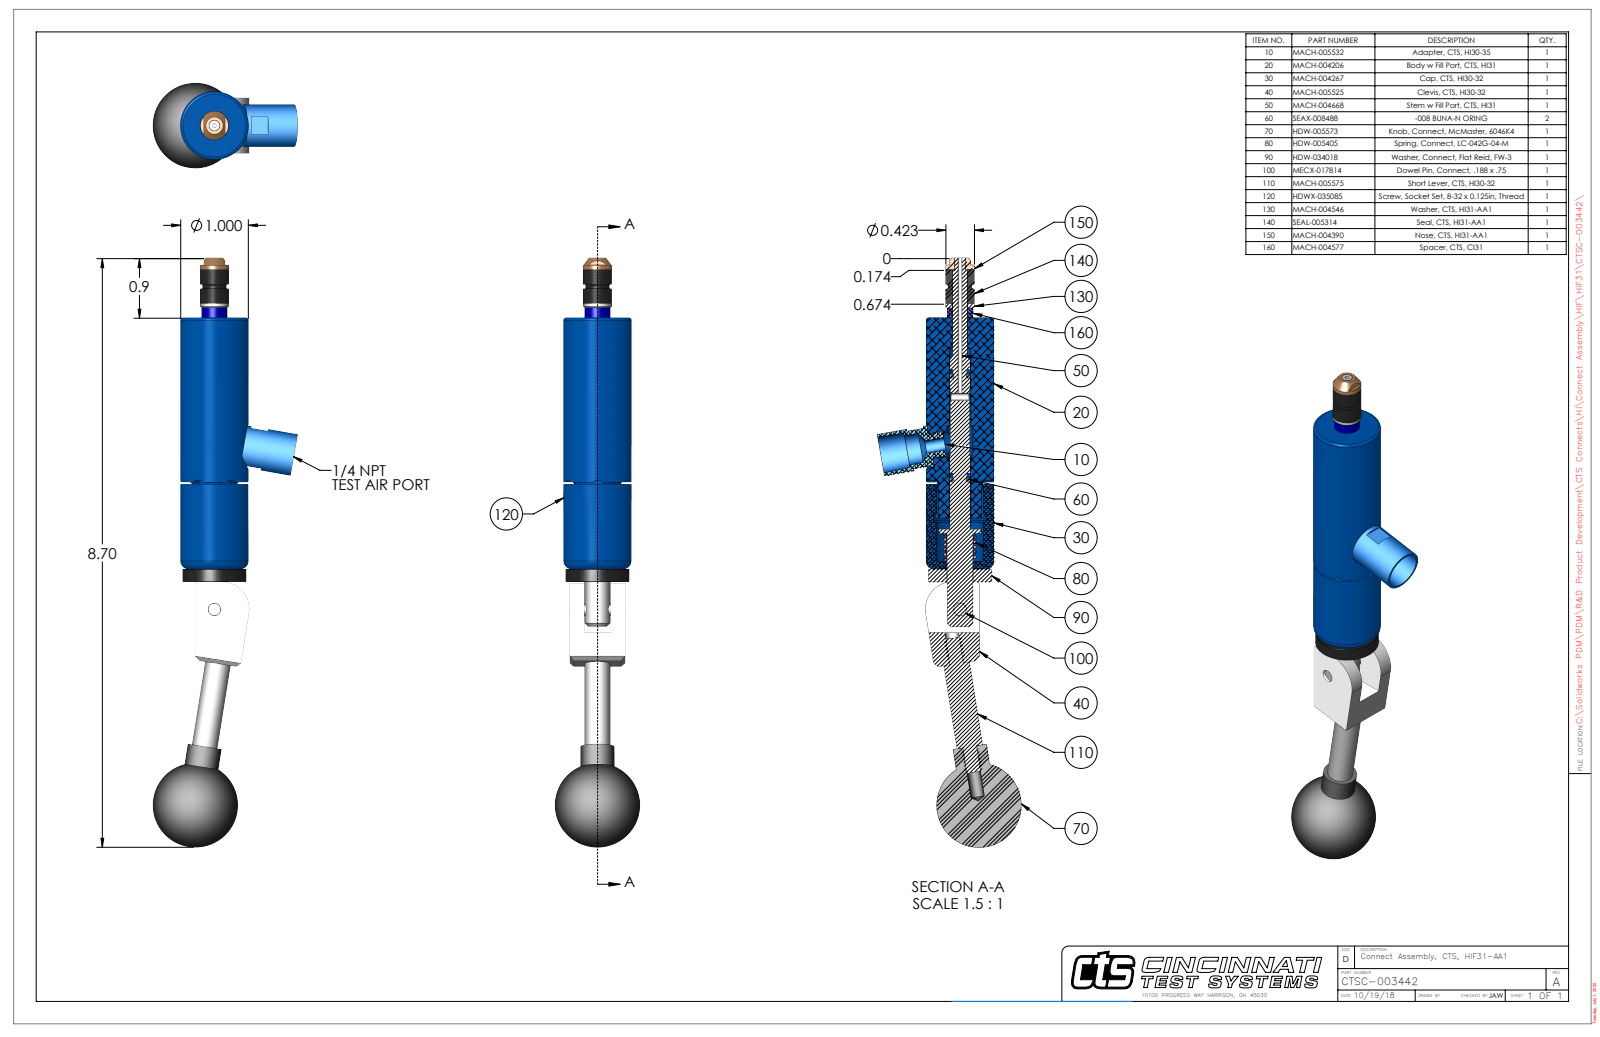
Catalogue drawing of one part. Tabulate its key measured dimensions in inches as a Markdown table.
| quantity | value |
| --- | --- |
| part name | CTSC-003442 |
| STEP written by | SolidWorks 2023 (AUTOMOTIVE_DESIGN) |
| units | inches |
| bodies | 10 solids, 281 faces (98 planar, 119 cylindrical, 64 other) |
| overall size | 8.704 × 2.128 × 1.25 |
| volume | 4.973 in³ |
| surface area | 38.05 in² |
| round holes (diameter × count) | 0.201 × 2, 0.063 × 1, 0.109 × 1, 0.136 × 1, 0.15 × 1, 0.159 × 1, 0.187 × 1, 0.189 × 1, 0.218 × 1, 0.228 × 1, 0.229 × 1, 0.385 × 1 |
| round bosses / shafts (diameter × count) | 1 × 1, 0.936 × 1, 0.62 × 1, 0.5 × 1, 0.423 × 1, 0.38 × 1, 0.379 × 1, 0.375 × 1 |
| partial cylindrical surfaces (radius × count) | 0.093 × 6, 0.029 × 2, 0.059 × 1, 0.325 × 1, 0.4 × 1, 0.481 × 1 |
| main face-to-face distances | 0.21, 0.602, 0.812, 0.187, 3.713, 3.901, 0.391, 2.46, 1.253, 1.441 |
| hole center spacings | 0.599, 1.658, 2.252 |
